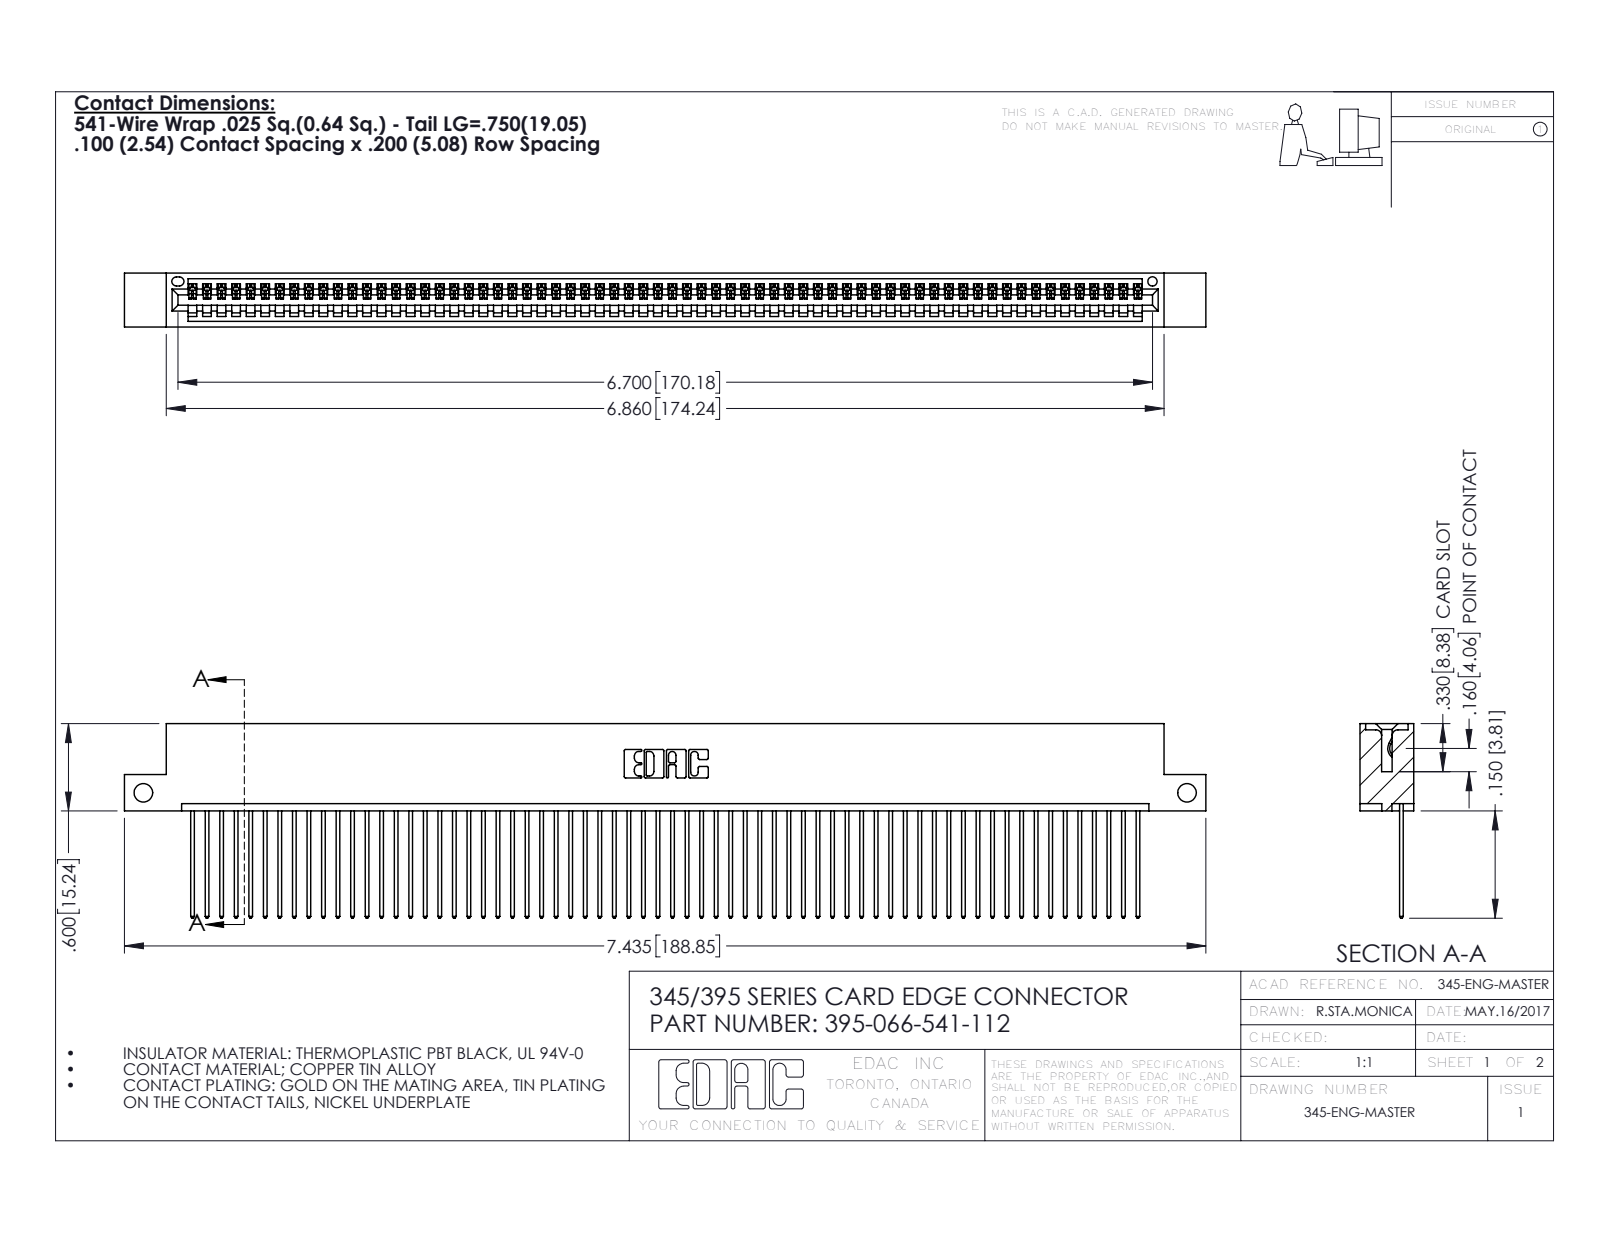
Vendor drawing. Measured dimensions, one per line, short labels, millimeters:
name: 395-066-541-112; 345-292-001_345-293-141; 345 Part_Flush Mounting Lugs - Side Mount
written by: SolidWorks 2016 (CONFIG_CONTROL_DESIGN)
unit: mm
bodies: 67 solids, 3954 faces (2720 planar, 1234 cylindrical, 0 other)
size: 188.8 × 34 × 9.4
volume: 18 270 mm³; area: 25 740 mm²
holes: 2× ⌀3.3, 1× ⌀1.6
rounds: 132× R0.2, 132× R0.3, 22× R0.3, 6× R0.2, 6× R0.8, 3× R0.7, 2× R0.8, 2× R1
face distances: 1.8, 7.6, 2.5, 6.9, 0.6, 9.4, 5.1, 5.7, 3.8, 1.8
hole spacings: 182.2
